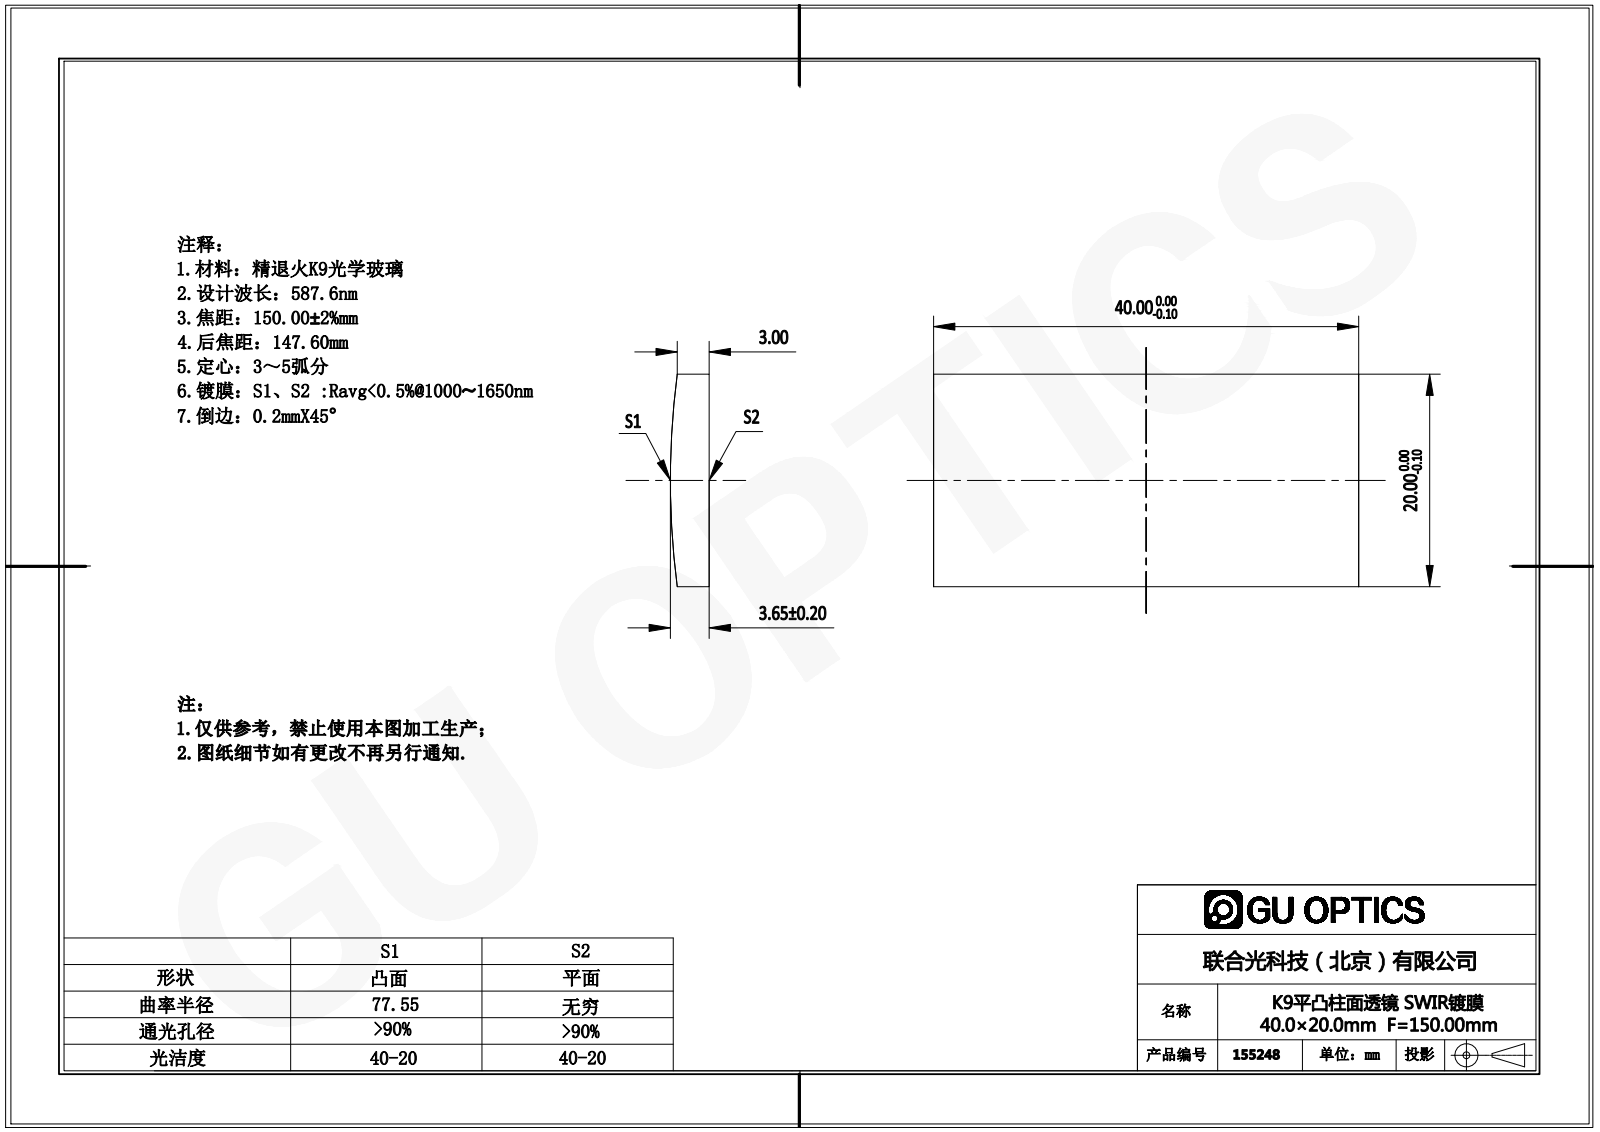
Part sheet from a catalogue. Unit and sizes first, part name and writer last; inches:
Units: inches
Overall size (bounding box): 1.575 × 0.787 × 0.144
Partial cylindrical surfaces — rounded edges, fillets, slot ends (radius × count): R3.053 ×1
Main face-to-face distances: 0.787, 1.575
Volume: 0.168 in³ · Surface area: 3.069 in²
Bodies: 1 solid, 6 faces (5 planar, 1 cylindrical, 0 other)
Part name (STEP PRODUCT): 155050
STEP written by: SolidWorks 2016 (AUTOMOTIVE_DESIGN)
